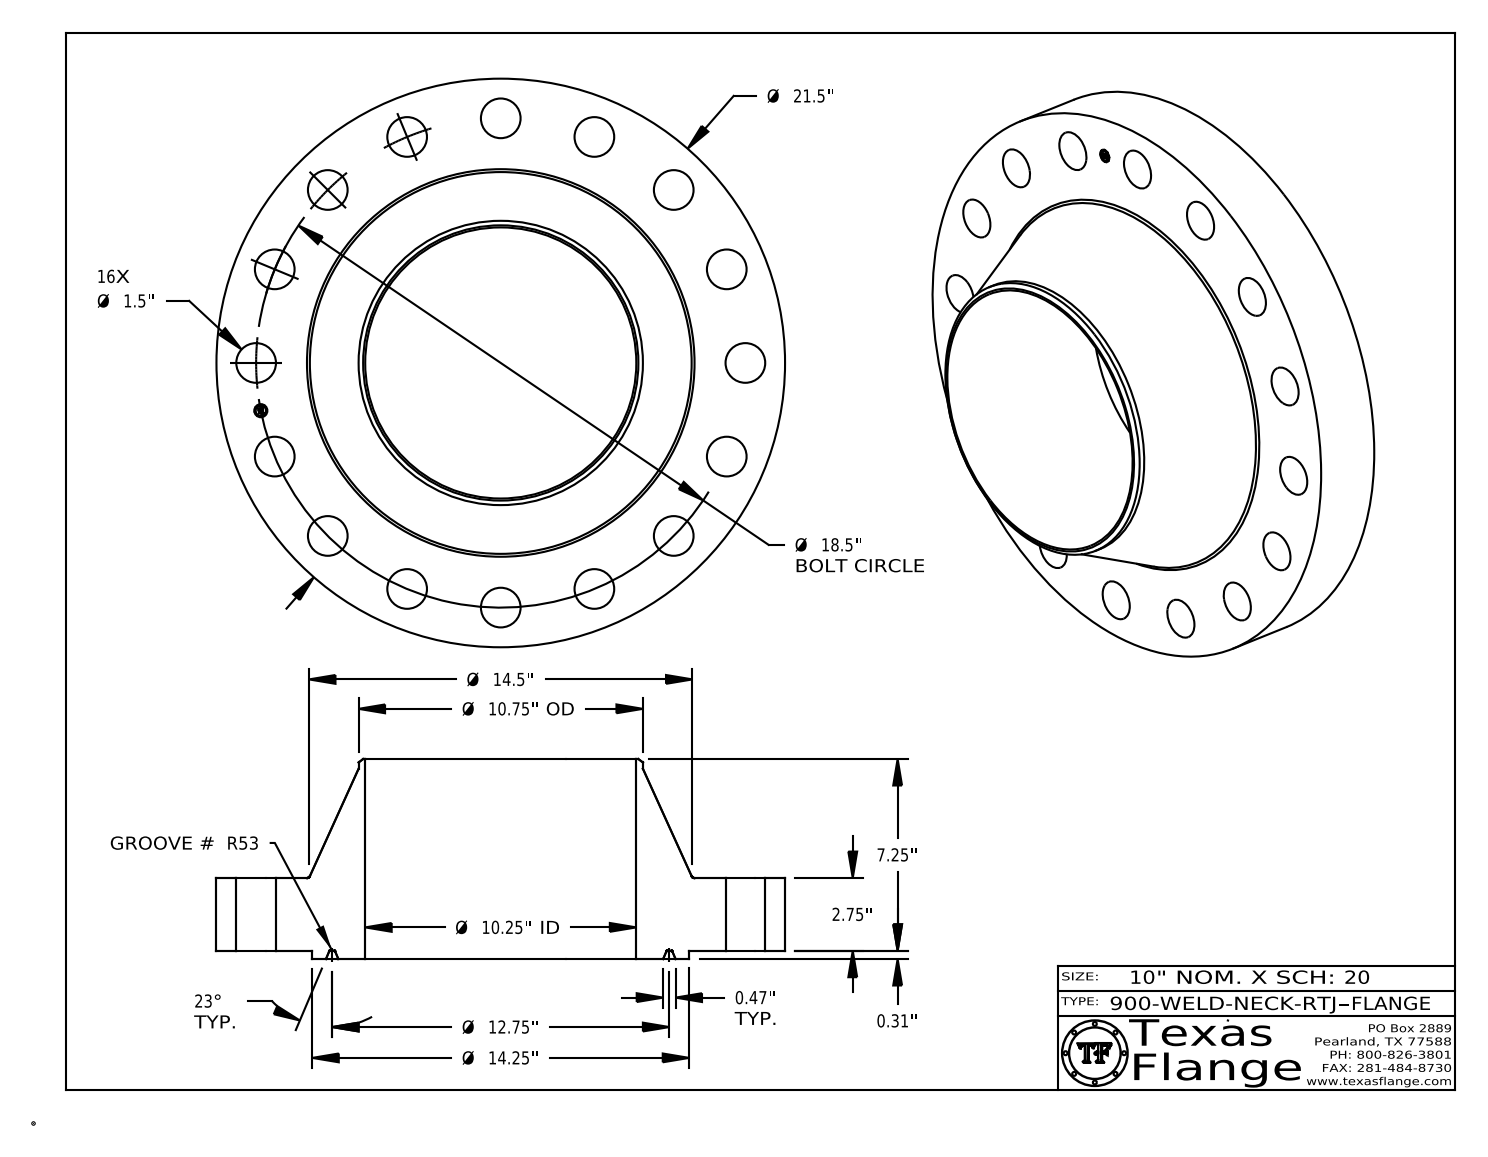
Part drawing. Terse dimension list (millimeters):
name: 900-WELD-NECK-RTJ
written by: CATIA V5 STEP AP214 (AUTOMOTIVE_DESIGN)
unit: mm
bodies: 1 solid, 445 faces (371 planar, 60 cylindrical, 14 other)
size: 546.1 × 546.1 × 192.1
volume: 14 690 000 mm³; area: 829 700 mm²
holes: 16× ⌀38.1, 1× ⌀12.6, 1× ⌀260.4
bosses: 8× ⌀0.8, 1× ⌀546.1, 1× ⌀362, 1× ⌀273.1, 1× ⌀9.9
face distances: 69.9, 8, 77.8, 192.1, 184.2, 114.3, 77.4, 69.5, 0.4, 114.7
hole spacings: 390.7, 179.8, 235, 332.3, 91.7, 91.7, 261.1, 261.1
